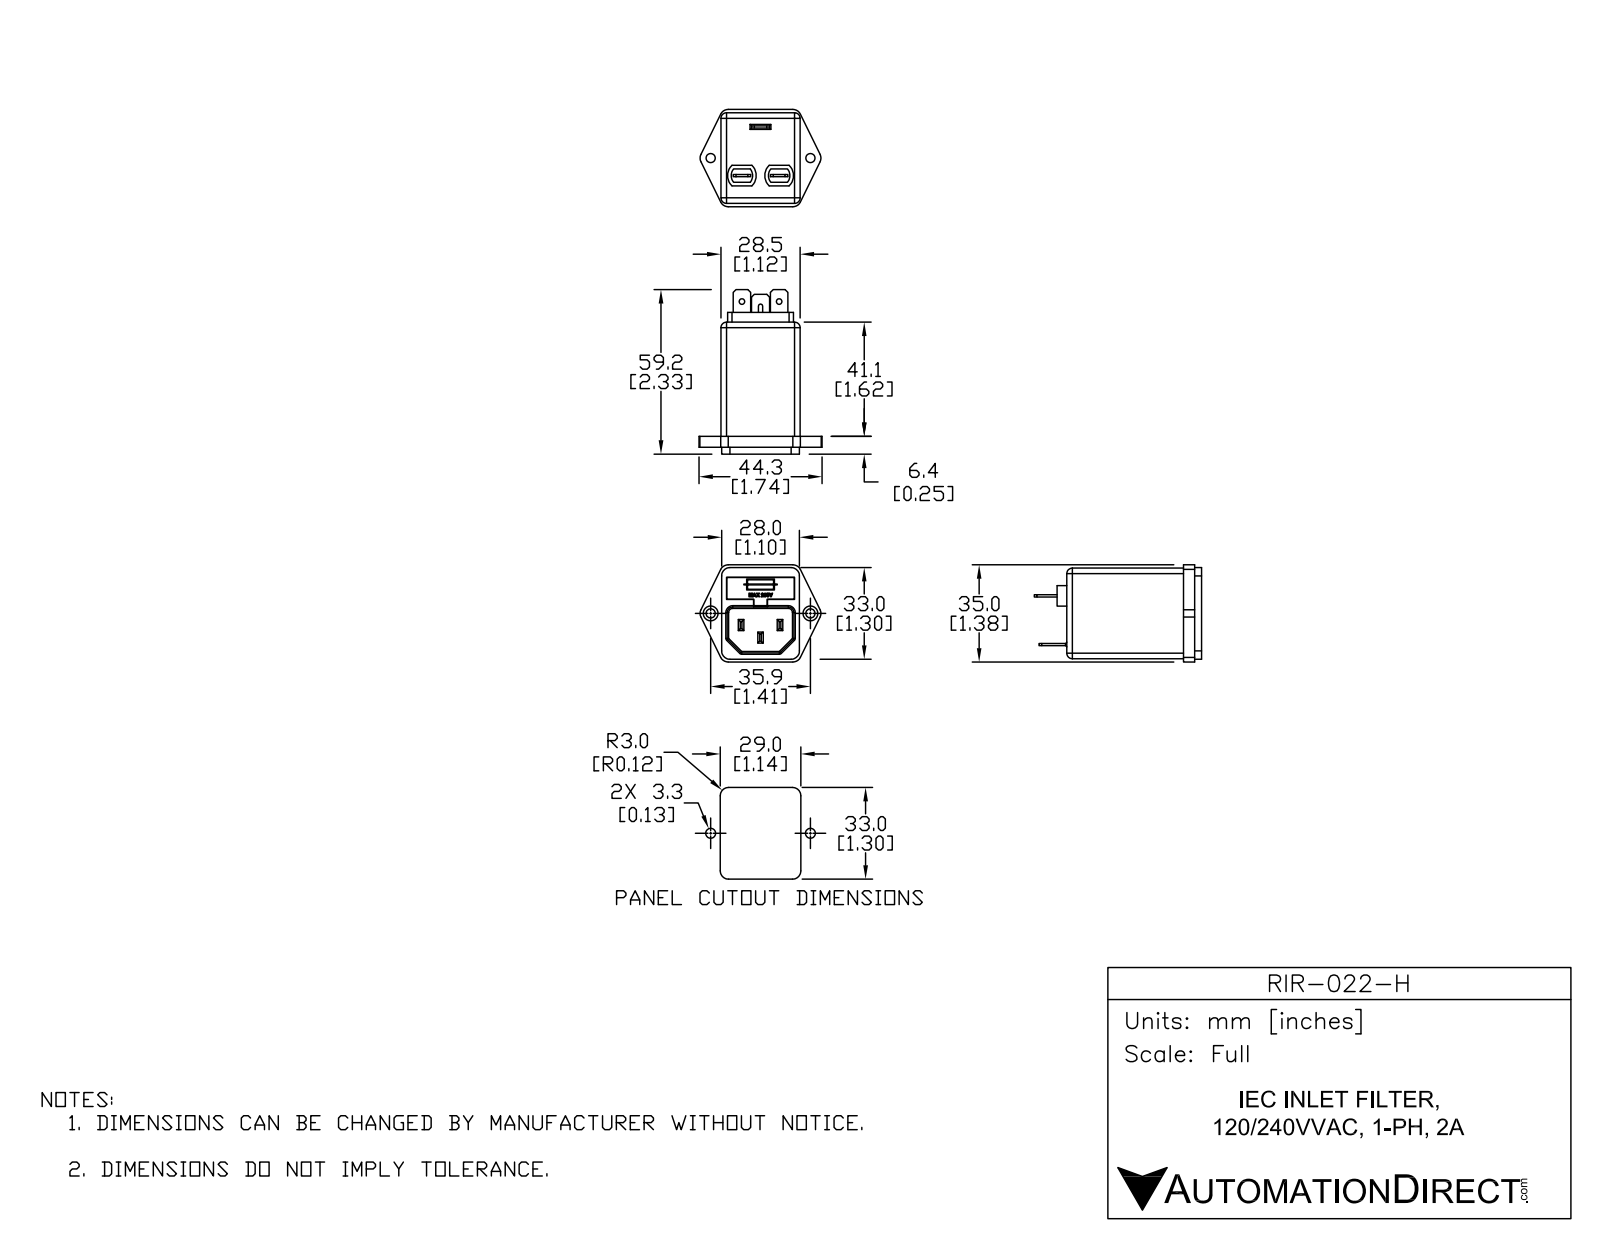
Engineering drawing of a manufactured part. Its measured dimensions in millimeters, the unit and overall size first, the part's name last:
Units: millimetres
Overall size (bounding box): 60.2 × 43.86 × 35
Round holes (diameter × count): ⌀2 ×2, ⌀3.3 ×2
Partial cylindrical surfaces — rounded edges, fillets, slot ends (radius × count): R0.5 ×20, R2 ×10, R0.75 ×2, R3.85 ×2, R5.15 ×2, R3 ×1
Main face-to-face distances: 28.5, 32.6, 14, 16.5, 48.5, 2, 4, 6.5, 26.25, 32
Hole centre spacings: 13.4, 35.9
Volume: 40 598 mm³ · Surface area: 10 976 mm²
Bodies: 1 solid, 316 faces (209 planar, 56 cylindrical, 51 other)
Part name (STEP PRODUCT): RIR0222H
STEP written by: SolidWorks 2015 (AUTOMOTIVE_DESIGN)
